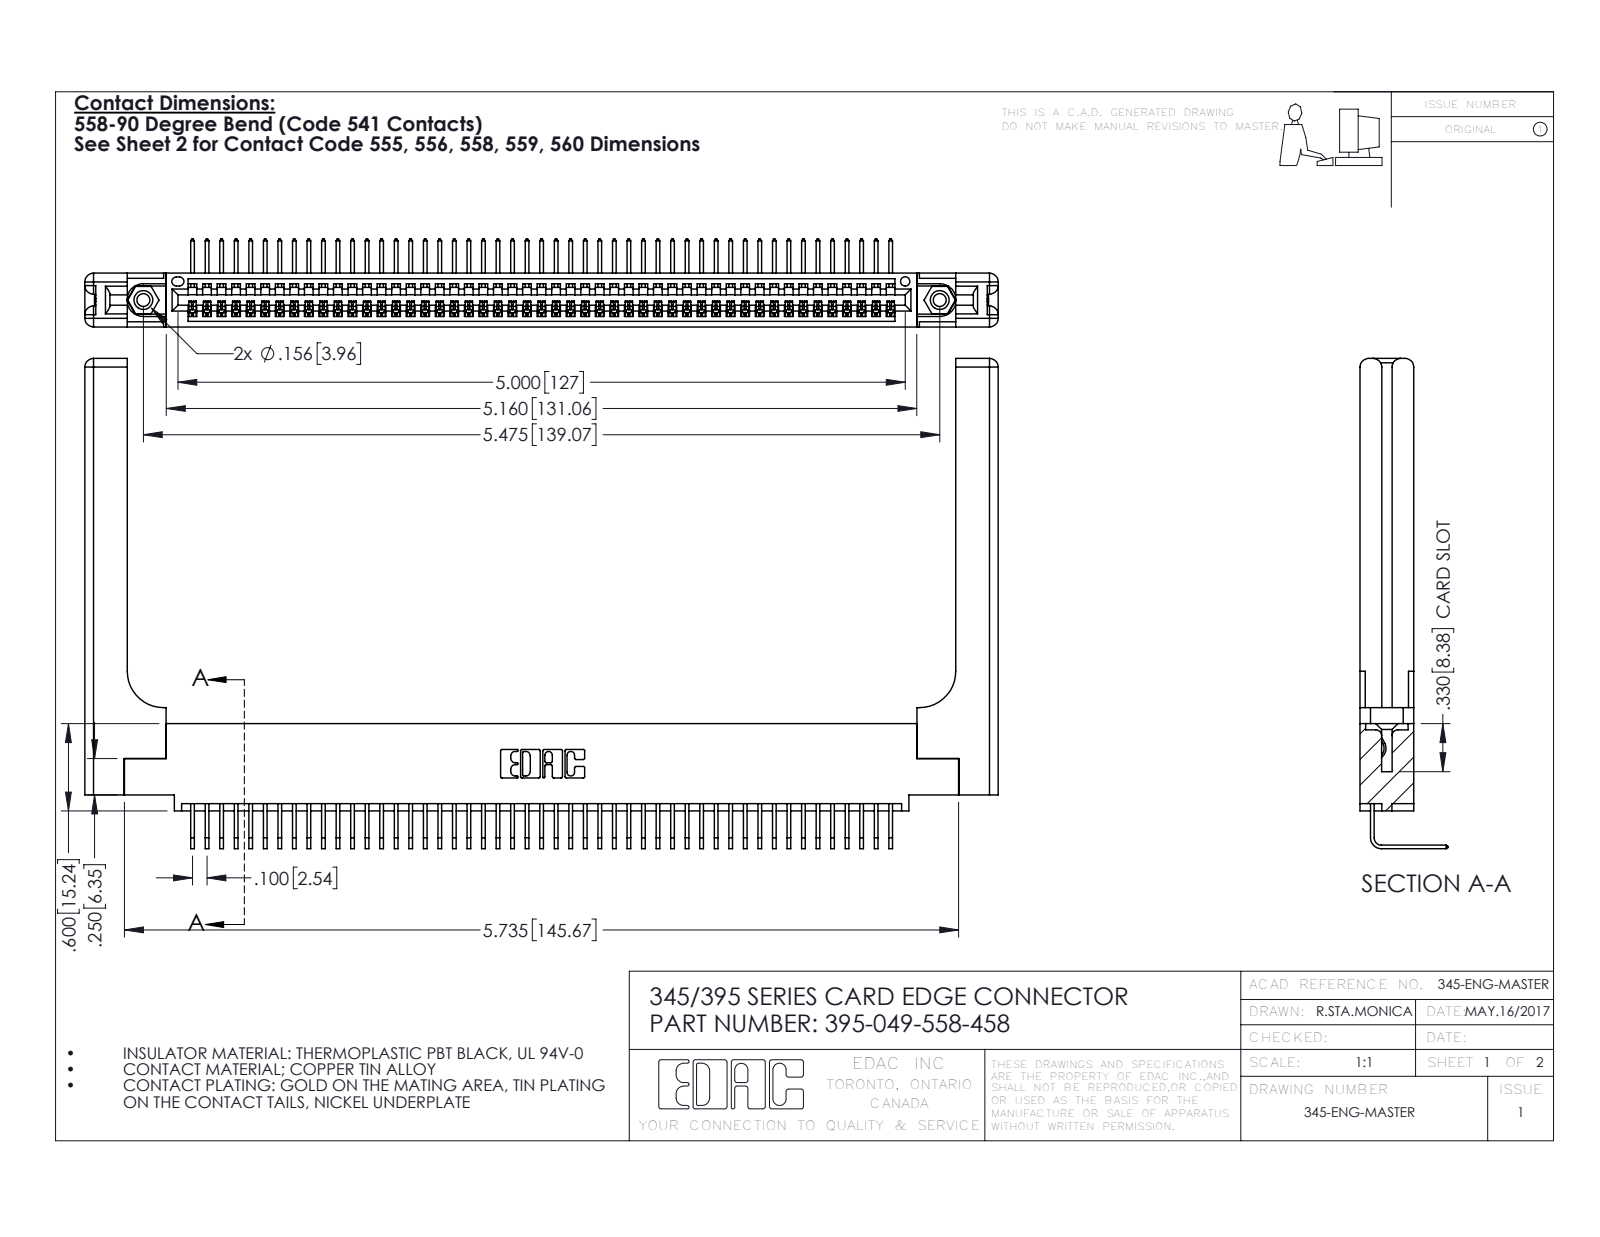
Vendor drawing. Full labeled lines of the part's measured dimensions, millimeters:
Part name (STEP PRODUCT): 345 Part_0.110 Offset - 0.156 Dia-TH; 345-292-001_558 Tail - 2; 345-220-058_345-220-058; 345-250-001_345-250-001-102 (+1 more)
STEP written by: SolidWorks 2016 (CONFIG_CONTROL_DESIGN)
Units: millimetres
Bodies: 54 solids, 3326 faces (2290 planar, 976 cylindrical, 60 other)
Overall size (bounding box): 159.5 × 85.6 × 15.4
Volume: 23 790 mm³ · Surface area: 26 770 mm²
Round holes (diameter × count): ⌀2.3 ×2, ⌀3.2 ×2, ⌀4 ×2, ⌀1.6 ×1
Round bosses / shafts (diameter × count): ⌀3.9 ×2
Partial cylindrical surfaces — rounded edges, fillets, slot ends (radius × count): R0.2 ×98, R0.3 ×22, R1.5 ×16, R0.2 ×6, R0.8 ×6, R0.7 ×3, R0.8 ×2, R0.8 ×2
Main face-to-face distances: 1.8, 9.4, 7.6, 2.5, 6.9, 0.6, 5.1, 5.7, 3.8, 3.8
Hole centre spacings: 6.9, 133.1, 139.1
